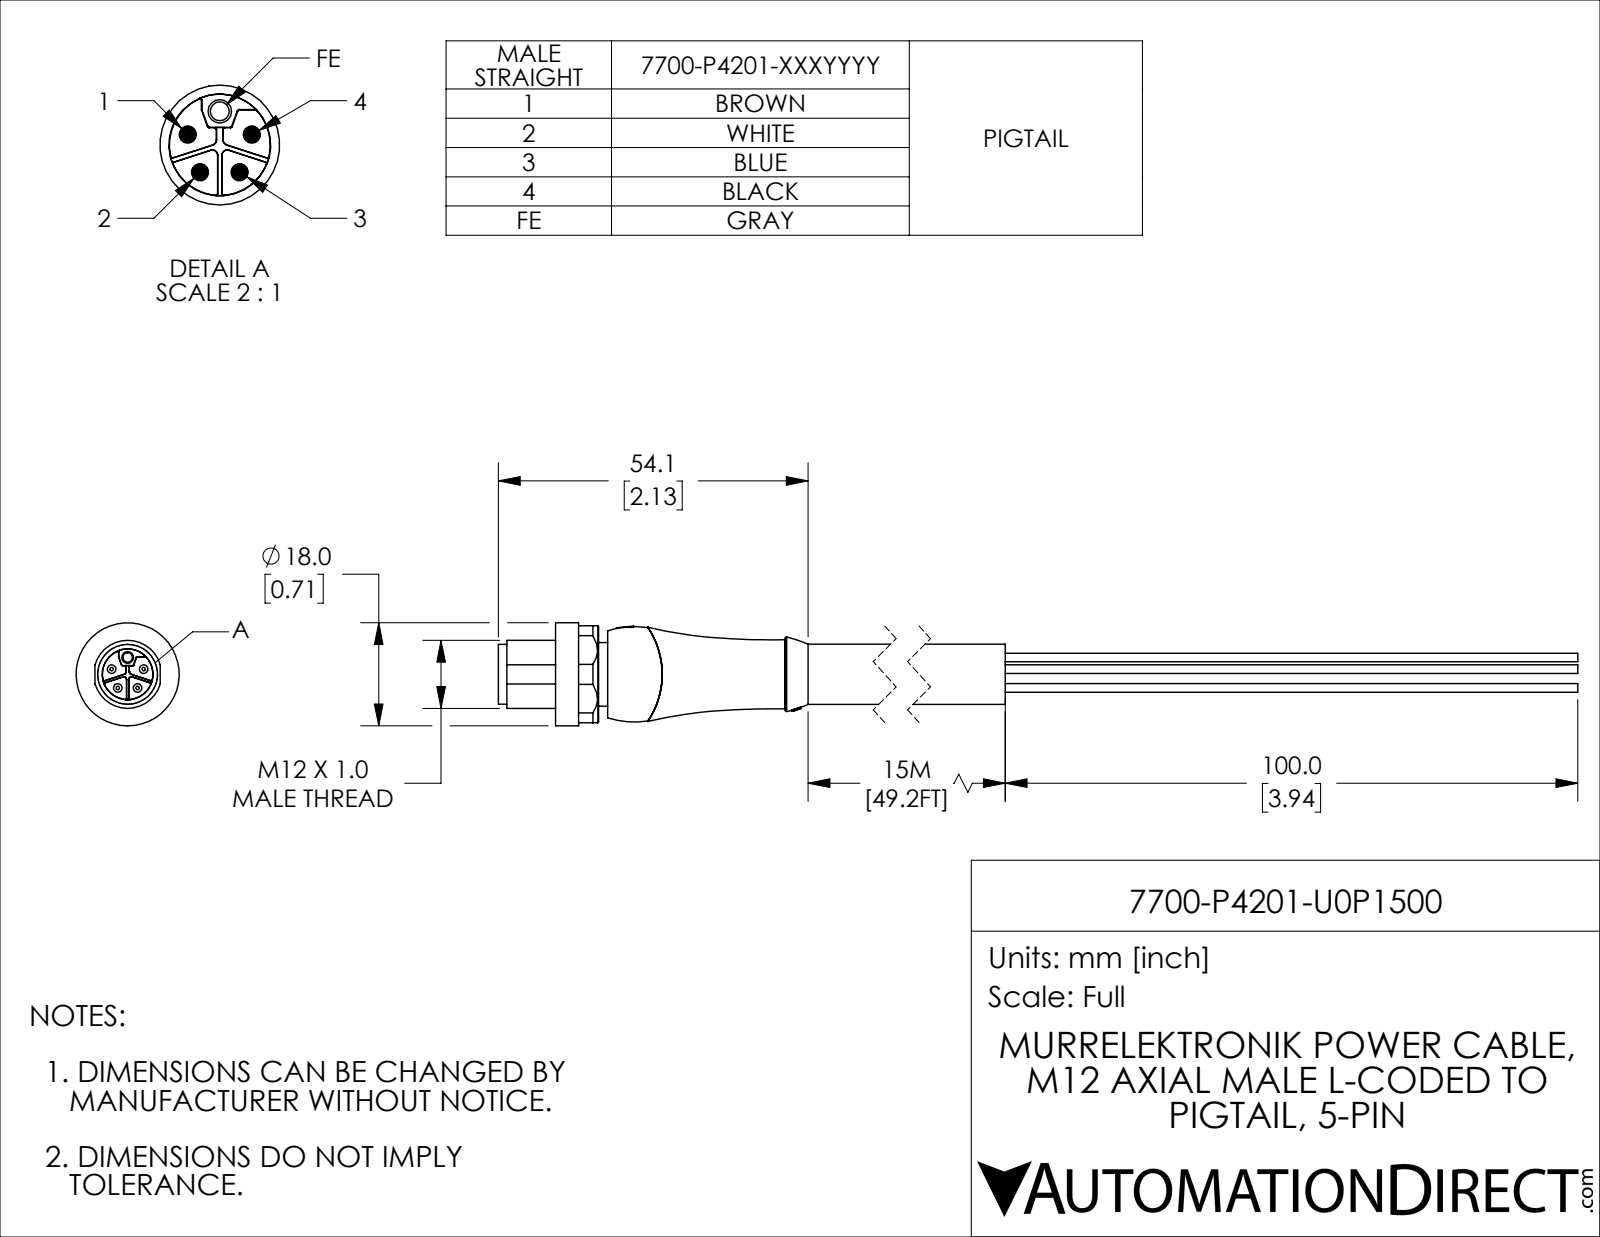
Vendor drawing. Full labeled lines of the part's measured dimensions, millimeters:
Part name (STEP PRODUCT): 7700-P4201-U0P1500
STEP written by: SolidWorks 2021 (CONFIG_CONTROL_DESIGN)
Units: millimetres
Bodies: 1 solid, 190 faces (87 planar, 51 cylindrical, 52 other)
Overall size (bounding box): 254.1 × 18 × 18
Volume: 17 489 mm³ · Surface area: 9 110 mm²
Round holes (diameter × count): ⌀1.65 ×1
Round bosses / shafts (diameter × count): ⌀1.5 ×5, ⌀18 ×1, ⌀11.88 ×1, ⌀11.1 ×1, ⌀10.5 ×1, ⌀10.45 ×1
Partial cylindrical surfaces — rounded edges, fillets, slot ends (radius × count): R0.15 ×6, R1.13 ×1, R8.95 ×1
Main face-to-face distances: 9.1, 1.9, 7.2, 144.1, 136.9, 135, 16.94, 1.2, 8.4, 10.3
